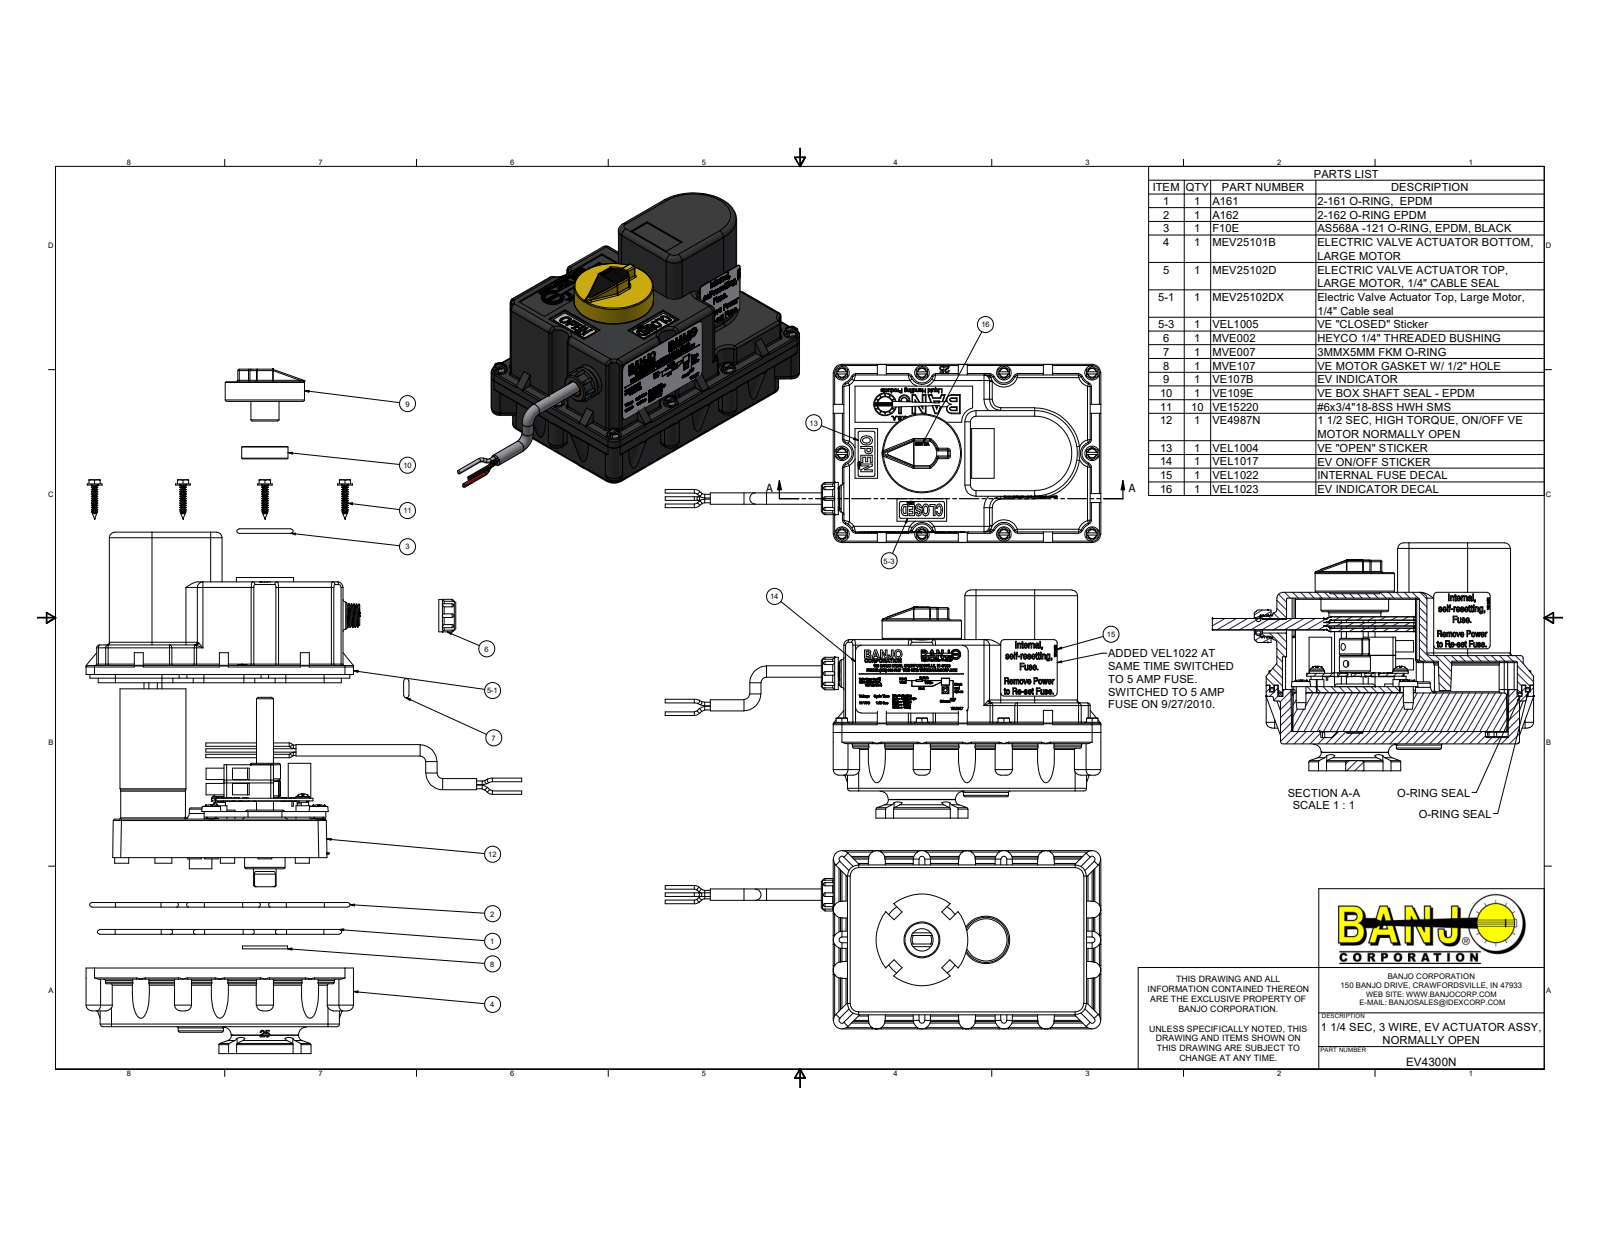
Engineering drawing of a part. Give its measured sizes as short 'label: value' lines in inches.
name: EV4300N; MEV25101B; MEV25102D; MEV25102DX (+8 more)
written by: Autodesk Inventor 2022 (AUTOMOTIVE_DESIGN)
unit: in
bodies: 50 solids, 10629 faces (5601 planar, 1127 cylindrical, 3901 other)
size: 9.656 × 5.055 × 3.95
volume: 41.69 in³; area: 418.1 in²
holes: 10× ⌀0.11, 10× ⌀0.16, 10× ⌀0.2, 8× ⌀0.052, 8× ⌀0.079, 6× ⌀0.047, 6× ⌀0.12, 6× ⌀0.15, 4× ⌀0.015, 4× ⌀0.089, 4× ⌀0.13, 4× ⌀0.136
bosses: 13× ⌀0.25, 10× ⌀0.328, 10× ⌀0.138, 9× ⌀0.08, 8× ⌀0.103, 6× ⌀0.315, 6× ⌀0.3, 5× ⌀0.075
rounds: 94× R0.03, 43× R0.035, 43× R0.06, 28× R0.125, 26× R0.02, 24× R0.315, 24× R0.5, 16× R0.39
face distances: 0.125, 3.355, 0.275, 0.79, 0.045, 3.23, 2.565, 1.225, 0.36, 2.955
hole spacings: 1.68, 2.058, 2.376, 1.785, 0.109, 0.348, 0.492, 1.188
